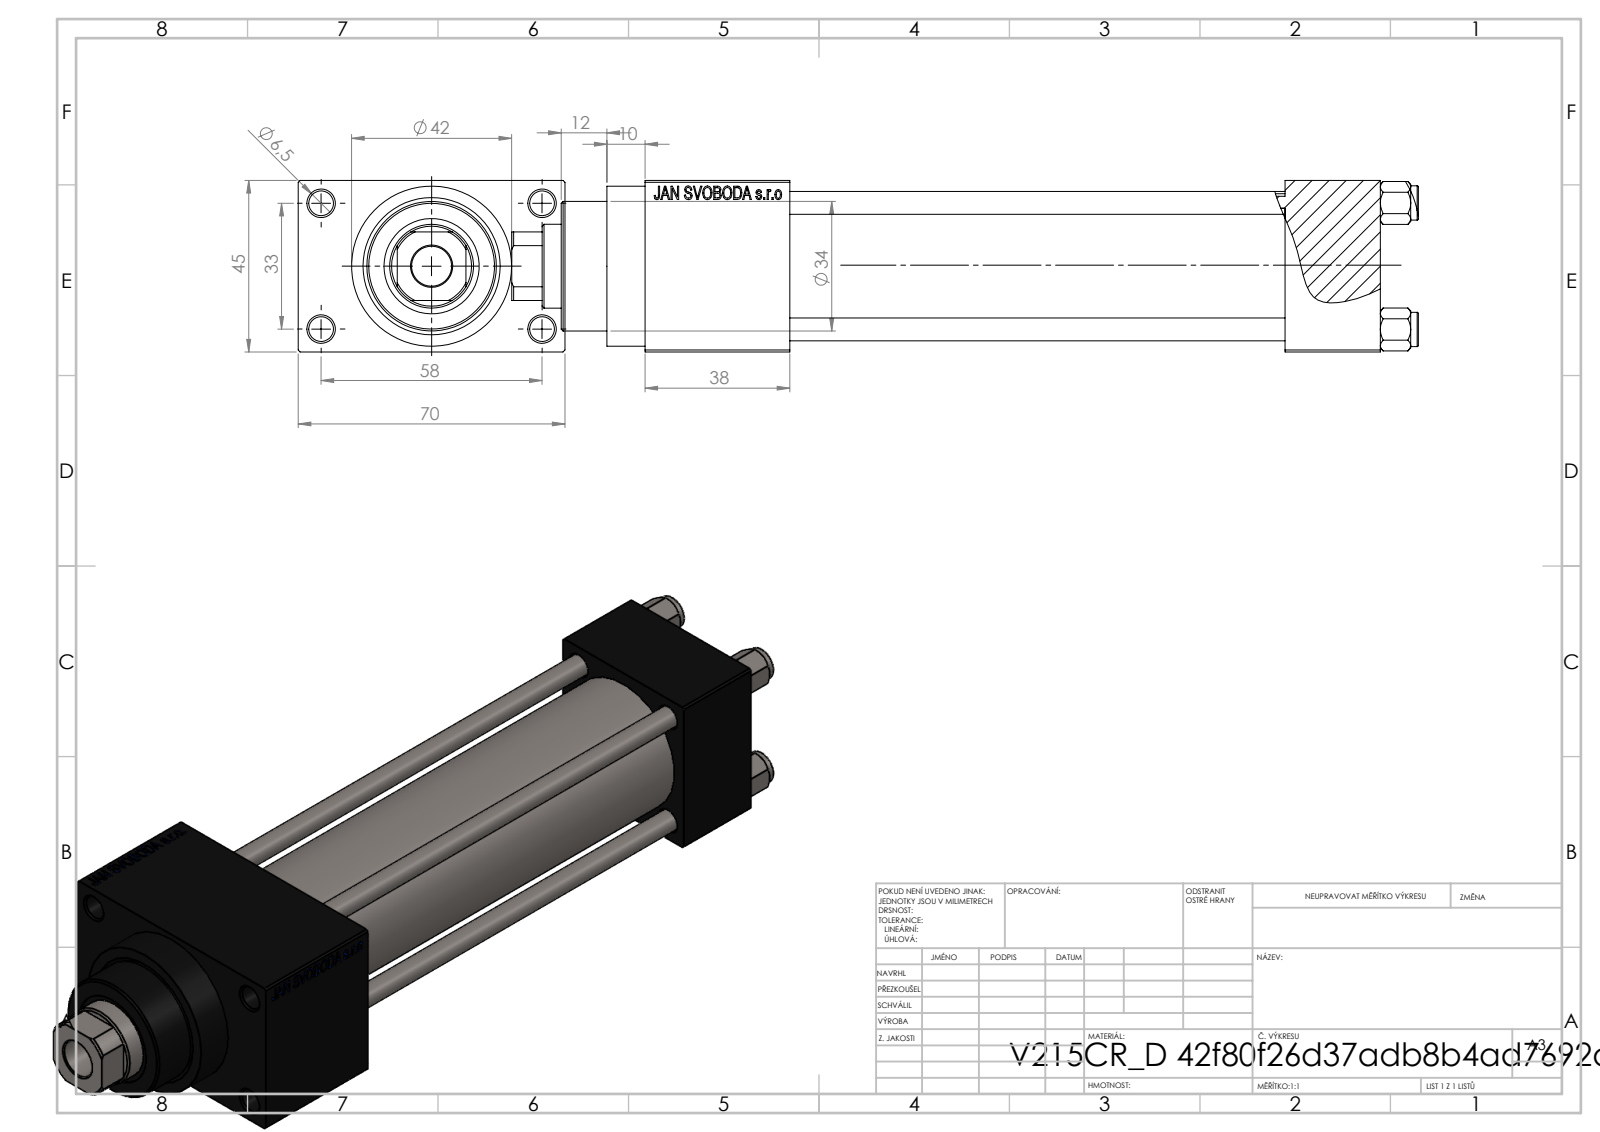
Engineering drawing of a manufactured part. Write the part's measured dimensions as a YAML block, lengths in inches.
part_name: "V215CR_VCP_D; V215CR_D_TYCINKA; V215CR_D_Body; NUT_M5_D (+1 more)"
step_written_by: "SolidWorks 2019 (CONFIG_CONTROL_DESIGN)"
units: inches
bodies: {solids: 10, faces: 209, planar: 59, cylindrical: 42, other: 108}
overall_size: [9.37, 1.75, 1.69]
volume: 8.293
surface_area: 68.12
round_holes:
  - {diameter: 0.236, count: 4}
  - {diameter: 0.413, count: 1}
  - {diameter: 0.866, count: 1}
  - {diameter: 0.984, count: 1}
round_bosses_or_shafts:
  - {diameter: 0.354, count: 4}
  - {diameter: 1.339, count: 1}
  - {diameter: 1.299, count: 1}
  - {diameter: 1.26, count: 1}
partial_cylinders:
  - {radius: 0.413, count: 1}
face_to_face_distances: [5.305, 1.181, 4.124, 7.48, 6.299, 2.176, 1.132, 0.383, 0.654, 7.992]
hole_center_spacings: [0.924, 1.307, 1.848]
